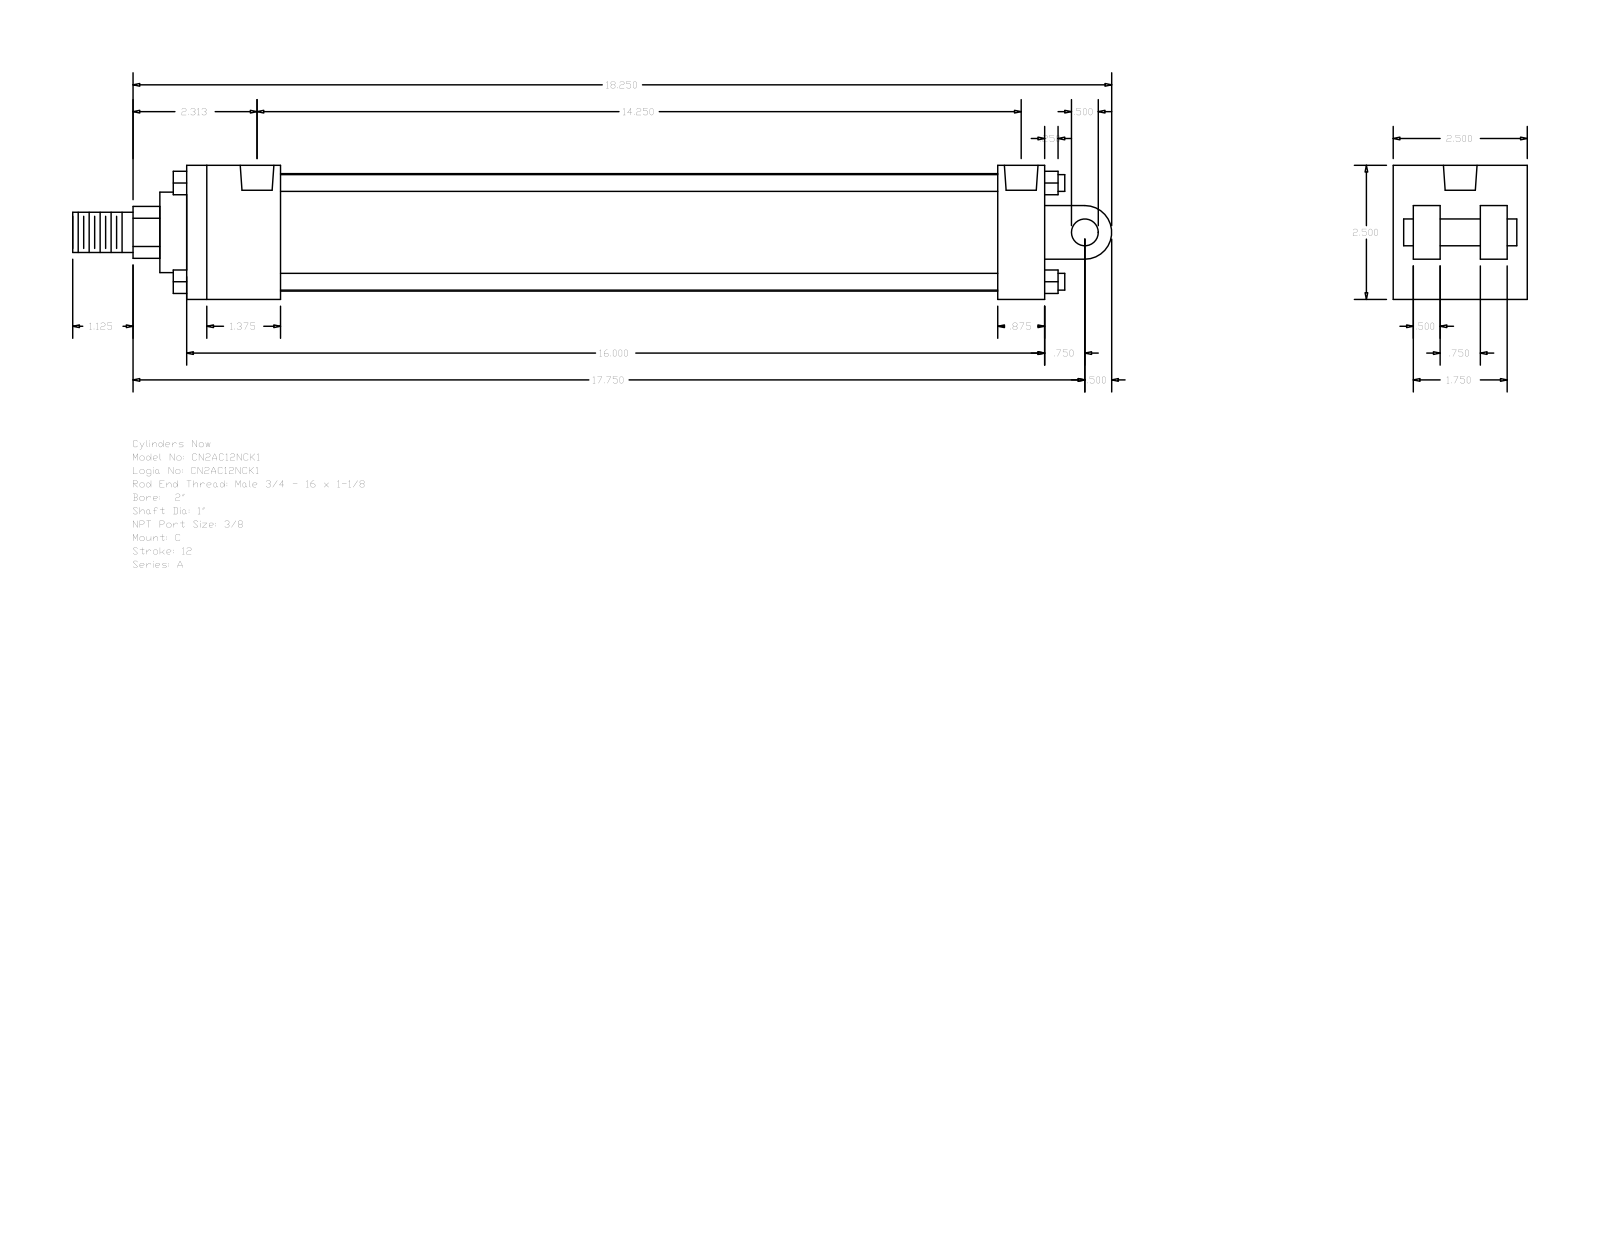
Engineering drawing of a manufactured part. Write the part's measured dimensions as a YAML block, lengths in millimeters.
part_name: "A_C__0200_1"
step_written_by: "GSSL Pune (CONFIG_CONTROL_DESIGN)"
units: millimeters
bodies: {solids: 0, faces: 135, planar: 102, cylindrical: 33, other: 0}
overall_size: [492.12, 63.5, 63.5]
round_holes:
  - {diameter: 5.56, count: 4}
  - {diameter: 15.93, count: 2}
round_bosses_or_shafts:
  - {diameter: 7.94, count: 4}
  - {diameter: 55.63, count: 1}
  - {diameter: 38.1, count: 1}
  - {diameter: 25.4, count: 1}
  - {diameter: 19.05, count: 1}
  - {diameter: 12.7, count: 1}
partial_cylinders:
  - {radius: 12.29, count: 1}
  - {radius: 12.7, count: 1}
face_to_face_distances: [63.5, 406.4, 44.45, 12.7, 9.52, 361.95, 384.17, 339.72, 22.23, 22.22]
hole_center_spacings: [356.38, 1.59, 3.98, 357.97, 360.36, 361.95]
